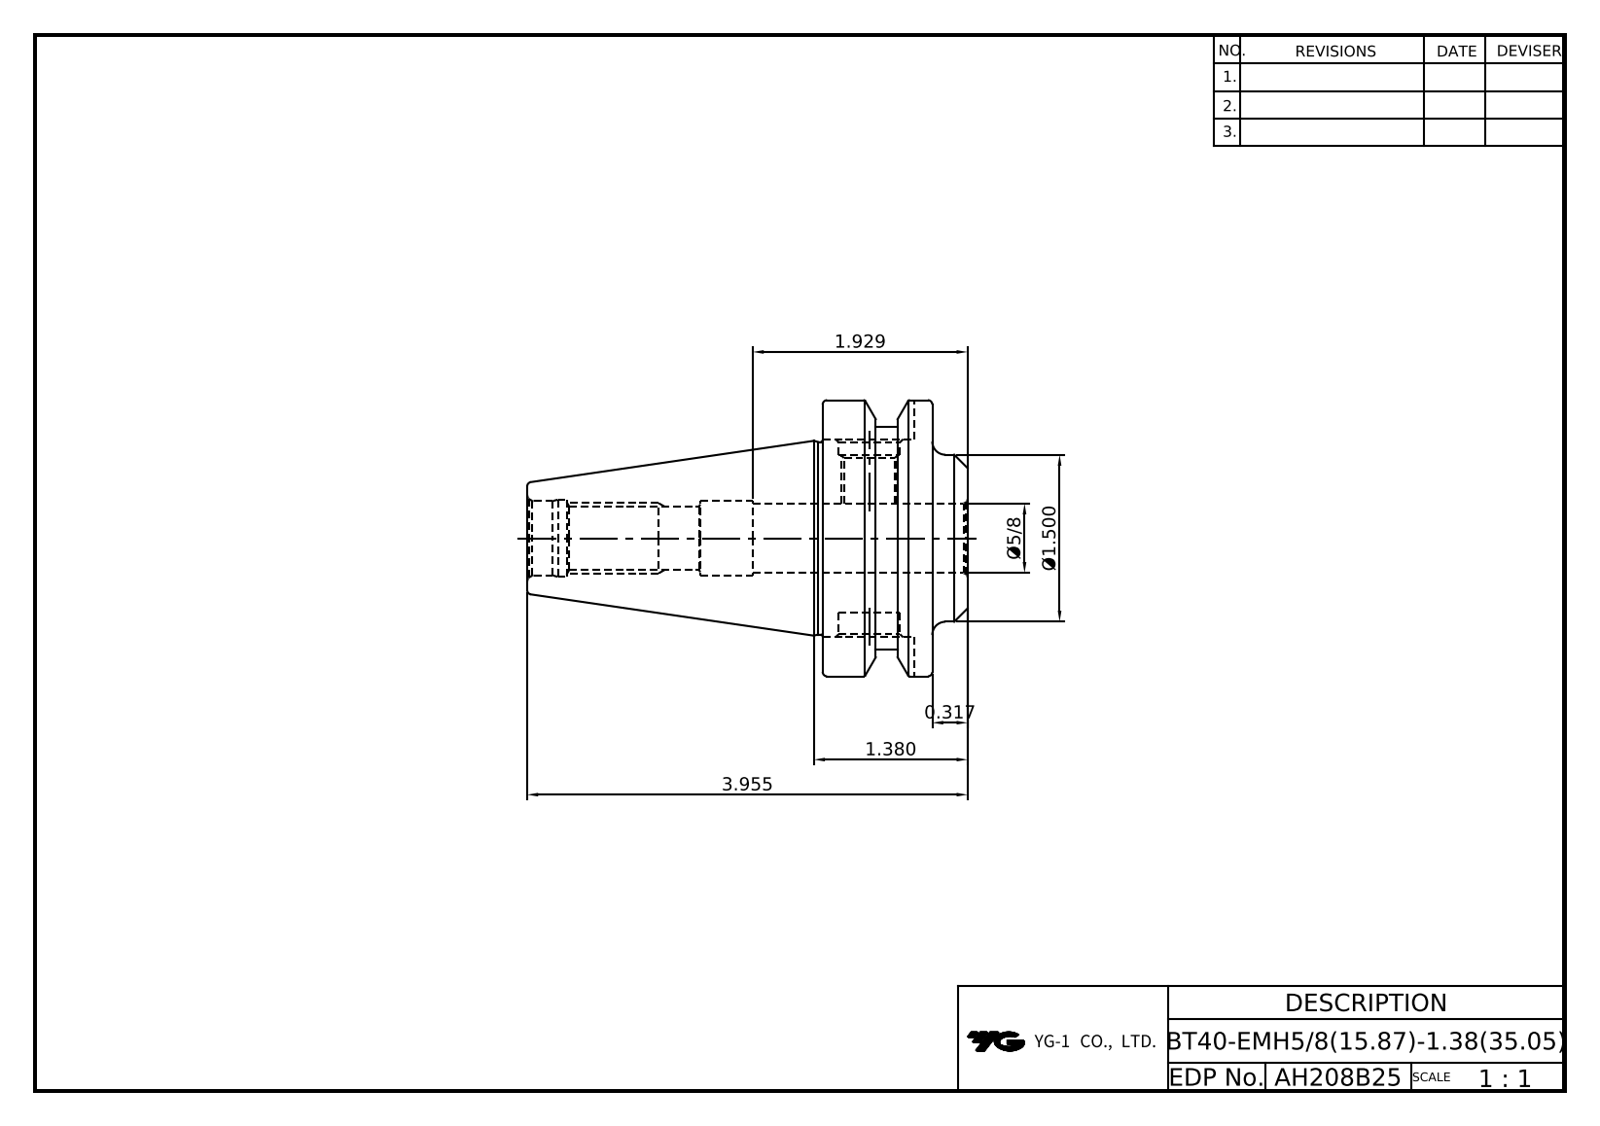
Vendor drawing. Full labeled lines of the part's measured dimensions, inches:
Part name (STEP PRODUCT): LO-BT40-EMH15.875-35.05
STEP written by: Autodesk Inventor 2022 (AUTOMOTIVE_DESIGN)
Units: inches
Bodies: 1 solid, 54 faces (20 planar, 17 cylindrical, 17 other)
Overall size (bounding box): 3.955 × 2.48 × 2.48
Volume: 7.366 in³ · Surface area: 38.22 in²
Round holes (diameter × count): ⌀0.446 ×1, ⌀0.545 ×1, ⌀0.551 ×1, ⌀0.625 ×1, ⌀0.669 ×1, ⌀0.672 ×1, ⌀0.693 ×1
Round bosses / shafts (diameter × count): ⌀2.48 ×1, ⌀2.008 ×1, ⌀1.732 ×1, ⌀1.5 ×1
Partial cylindrical surfaces — rounded edges, fillets, slot ends (radius × count): R0.317 ×1
Main face-to-face distances: 0.984, 1.301, 0.317, 0.628, 0.673, 0.311, 0.476, 0.197, 0.508, 0.825
